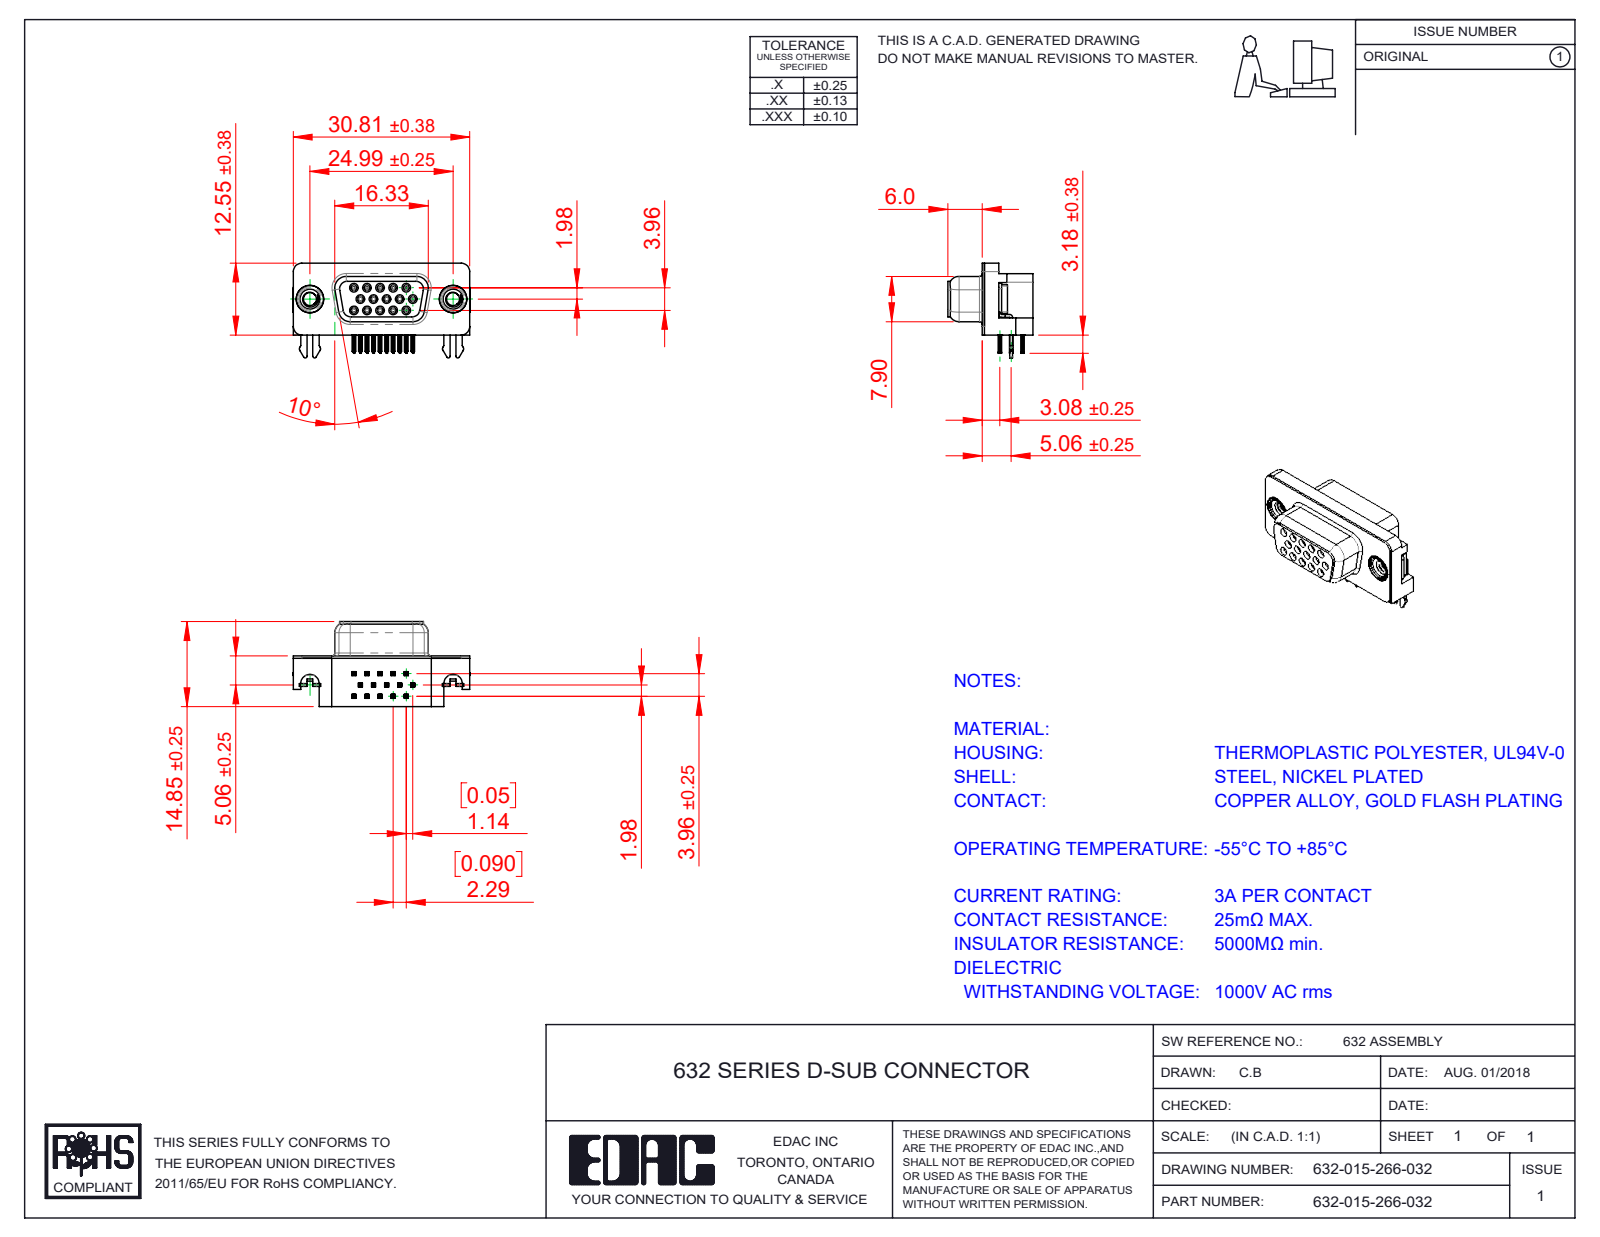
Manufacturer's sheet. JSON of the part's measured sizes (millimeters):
{"part_name": "632 Contact Top; 632 Contact Middle; 632 Contact Bottom; 632 Shell_9 Socket (+4 more)", "step_written_by": "SolidWorks 2016 (CONFIG_CONTROL_DESIGN)", "units": "millimeters", "bodies": {"solids": 21, "faces": 2338, "planar": 990, "cylindrical": 612, "other": 736}, "overall_size": [30.89, 16.55, 14.85], "volume_mm3": 2921, "surface_area_mm2": 5018, "round_holes": [[0.8, 15], [0.9, 15], [2.26, 2], [4, 2], [4.8, 2], [5, 2]], "round_bosses_or_shafts": [[1.2, 15], [4.9, 2], [4.75, 2], [3.9, 2]], "partial_cylinders_radius": [[0.1, 120], [0.15, 60], [0.35, 30], [0.34, 15], [1, 11], [0.28, 10], [0.5, 10], [0.25, 8]], "face_to_face_distances": [0.4, 1.98, 8.45, 8.85, 2.9, 2.5, 5.95, 6.4, 6.7, 7.05], "hole_center_spacings": [2.28, 2.29, 3.96, 4.57, 6.05, 3.97, 4.58, 6.86]}
